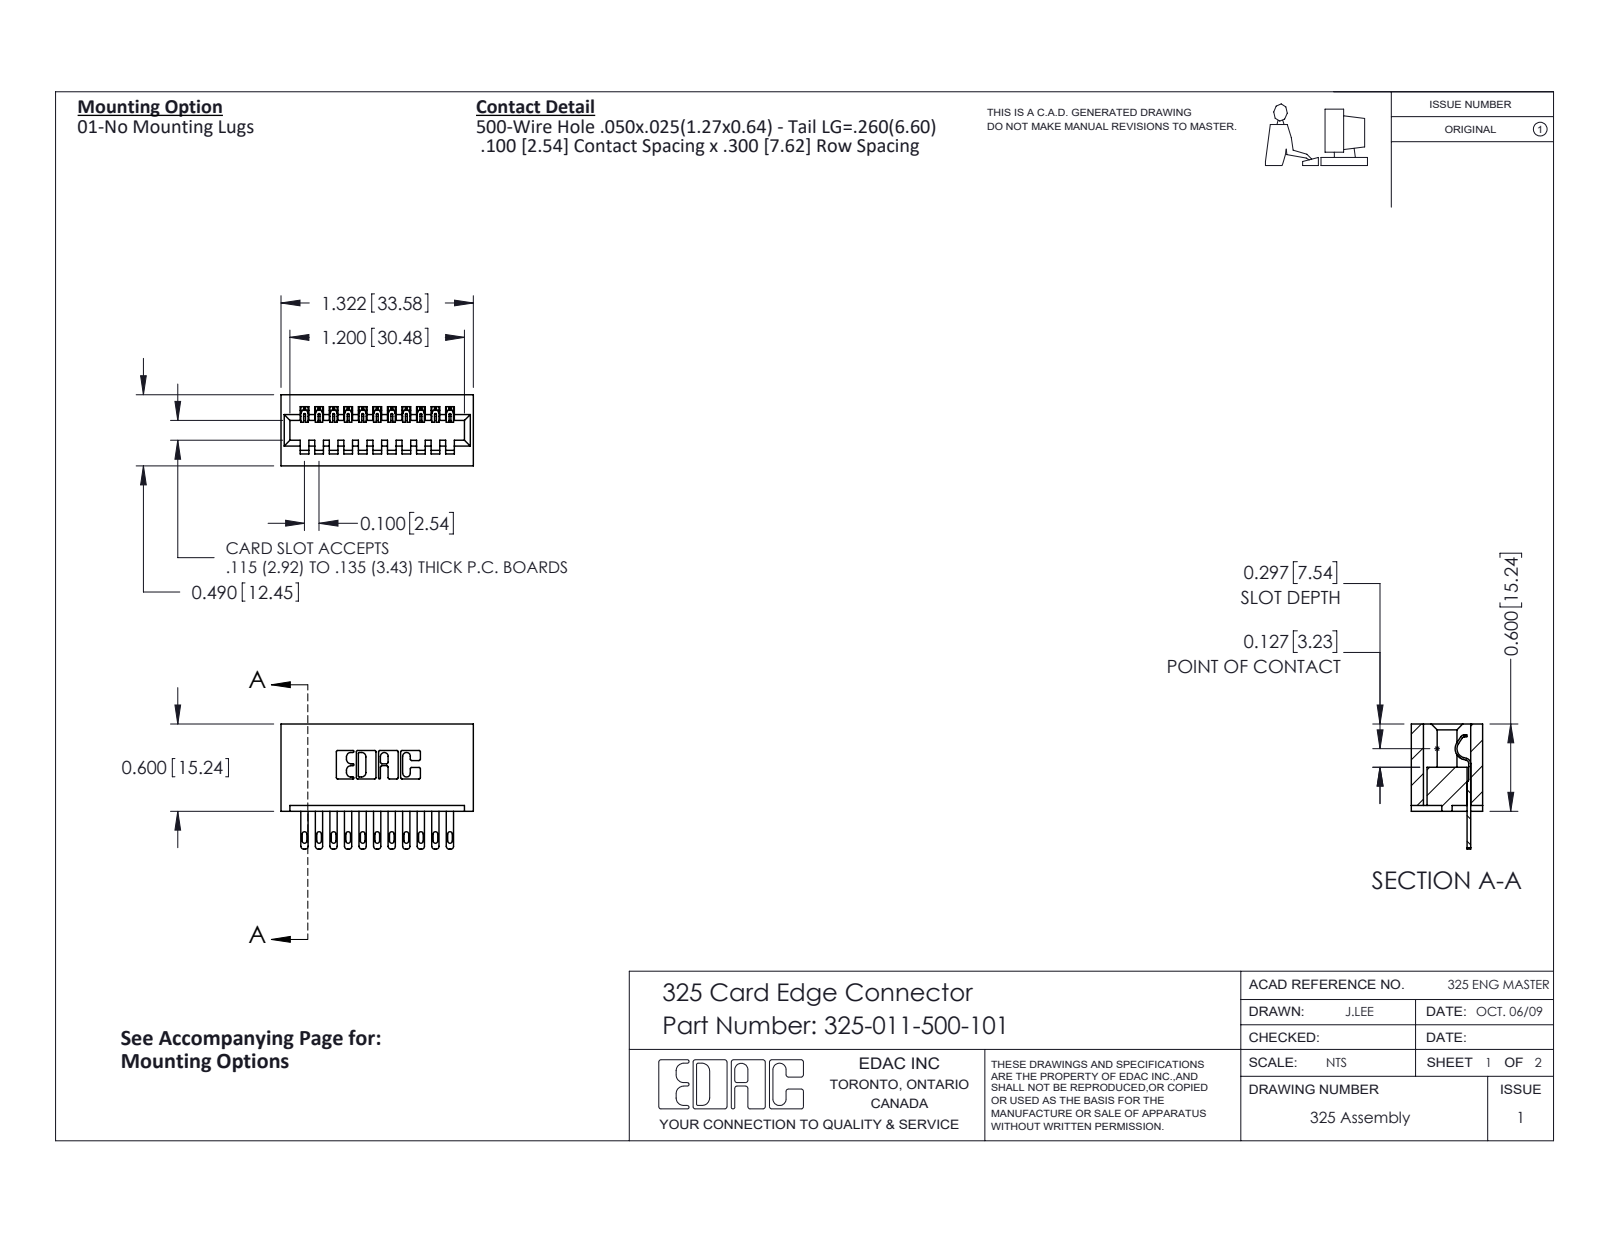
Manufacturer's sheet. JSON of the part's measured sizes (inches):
{"part_name": "325 Part_Lugless; 325-011-500-101; 325-292-001_325-293-100", "step_written_by": "SolidWorks 2016 (CONFIG_CONTROL_DESIGN)", "units": "inches", "bodies": {"solids": 12, "faces": 700, "planar": 462, "cylindrical": 238, "other": 0}, "overall_size": [1.322, 0.86, 0.49], "volume_in3": 0.281, "surface_area_in2": 7.77, "partial_cylinders_radius": [[0.006, 22], [0.01, 22], [0.016, 22], [0.02, 22], [0.007, 6], [0.031, 6], [0.026, 3], [0.014, 1]], "face_to_face_distances": [0.3, 0.083, 0.407, 0.1, 0.2, 0.49, 0.4, 0.04, 0.107, 0.383]}
